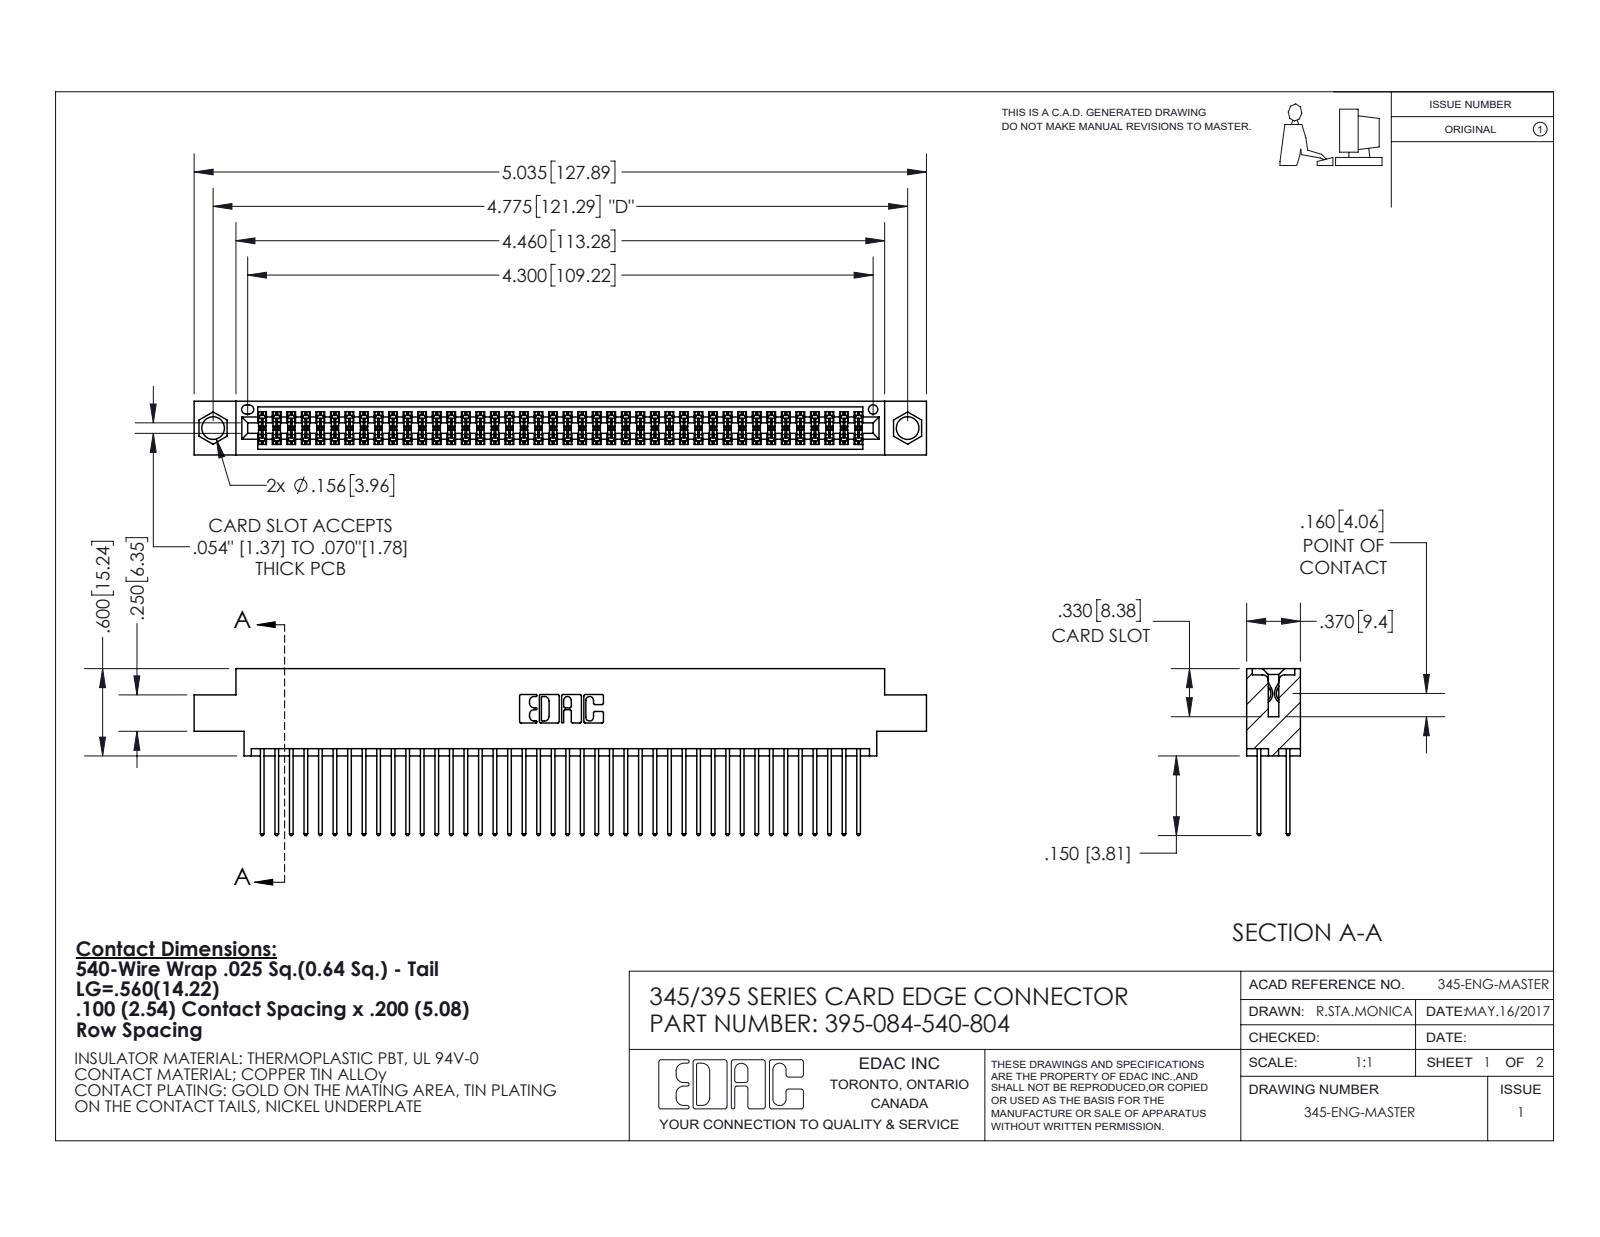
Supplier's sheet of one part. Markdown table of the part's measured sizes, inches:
| quantity | value |
| --- | --- |
| part name | 345-292-001_345-293-140; 395-084-540-804; 345 Part_0.170 Offset - 0.156 Dia-TI |
| STEP written by | SolidWorks 2020 (CONFIG_CONTROL_DESIGN) |
| units | inches |
| bodies | 85 solids, 4344 faces (2870 planar, 1474 cylindrical, 0 other) |
| overall size | 5.035 × 1.147 × 0.37 |
| volume | 0.764 in³ |
| surface area | 30.97 in² |
| round holes (diameter × count) | 0.156 × 2, 0.064 × 1 |
| partial cylindrical surfaces (radius × count) | 0.006 × 126, 0.01 × 84, 0.01 × 22, 0.007 × 6, 0.031 × 6, 0.026 × 3, 0.014 × 2, 0.019 × 2 |
| main face-to-face distances | 0.072, 0.298, 0.2, 0.098, 0.272, 0.025, 0.37, 0.225, 0.175, 0.149 |
| hole center spacings | 0.27, 4.539, 4.775 |
